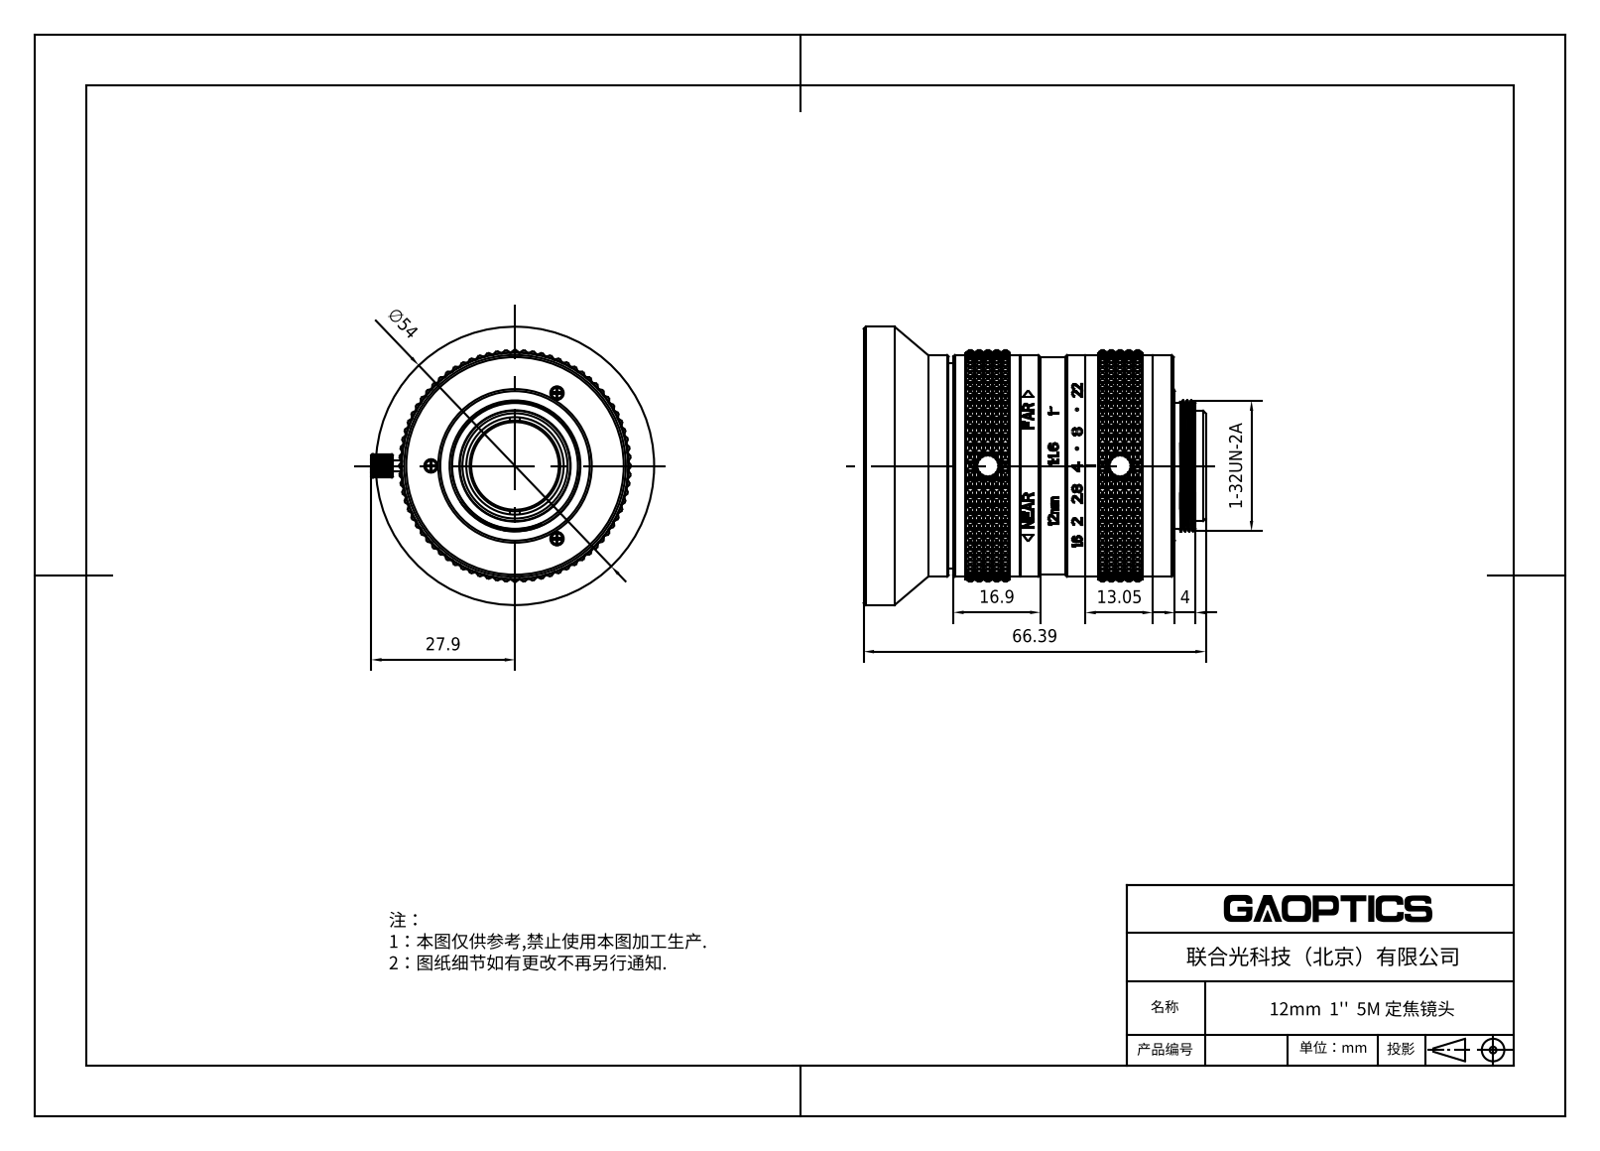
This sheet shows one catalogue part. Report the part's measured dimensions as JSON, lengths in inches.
{"part_name": "600027", "step_written_by": "SolidWorks 2020 (CONFIG_CONTROL_DESIGN)", "units": "inches", "bodies": {"solids": 3, "faces": 8469, "planar": 5450, "cylindrical": 1085, "other": 1934}, "overall_size": [2.628, 2.161, 2.126], "volume_in3": 5.132, "surface_area_in2": 54.86, "round_holes": [[0.102, 6], [0.035, 3], [0.063, 3], [0.071, 3], [0.039, 1], [0.043, 1], [0.669, 1], [0.693, 1], [0.744, 1], [0.776, 1], [0.85, 1], [1.319, 1]], "round_bosses_or_shafts": [[0.098, 3], [0.067, 3], [0.079, 2], [2.126, 1], [1.969, 1], [1.728, 1], [1.693, 1], [1.661, 1]], "partial_cylinders_radius": [[0.049, 6], [0.089, 2], [0.031, 1], [0.053, 1], [0.83, 1], [0.845, 1], [0.884, 1]], "face_to_face_distances": [1.981, 1.559, 1.531, 0.839, 0.017, 1.998, 0.368, 0.351, 1.63, 0.846], "hole_center_spacings": [0.642, 0.119, 0.615, 0.708, 0.761, 0.8, 1.111, 1.399]}
